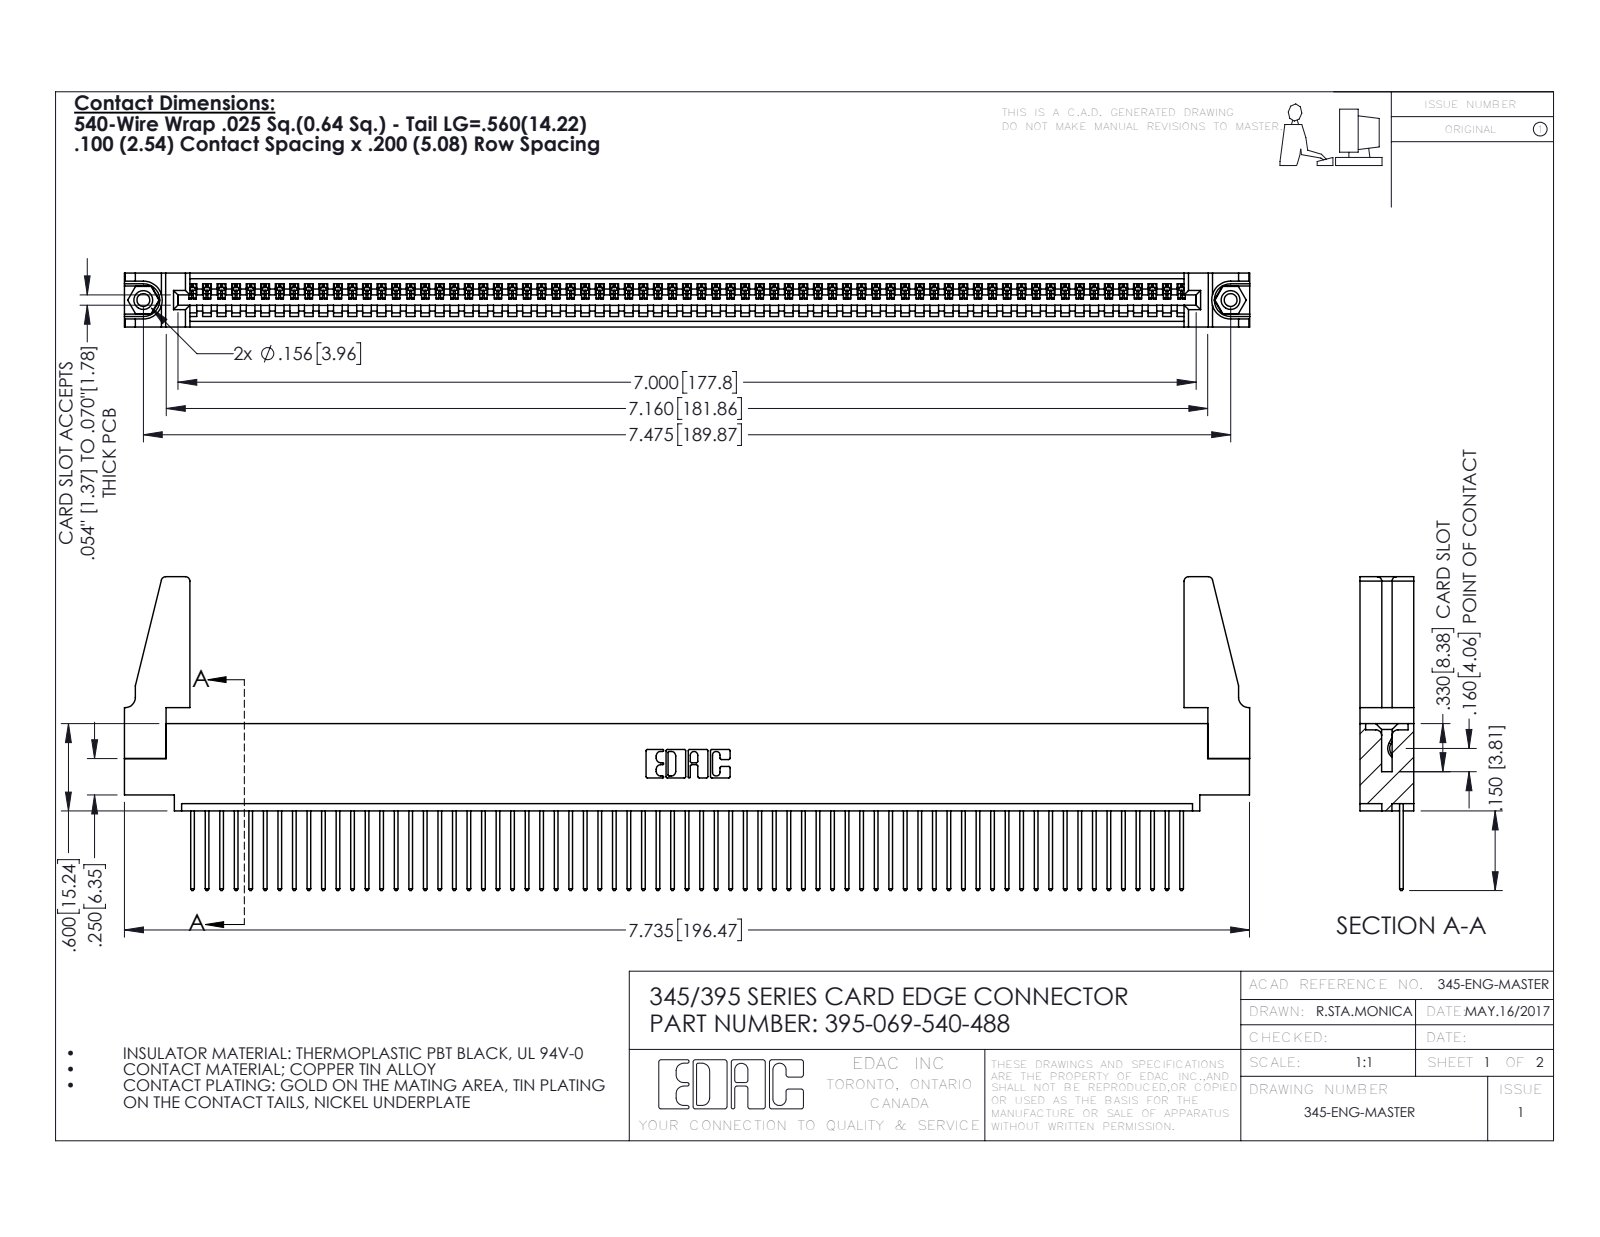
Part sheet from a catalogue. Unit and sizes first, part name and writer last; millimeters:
Units: millimetres
Overall size (bounding box): 196.5 × 54.8 × 9.4
Round holes (diameter × count): ⌀2.3 ×2, ⌀3.2 ×2, ⌀4 ×2, ⌀1.6 ×1
Round bosses / shafts (diameter × count): ⌀3.9 ×2
Partial cylindrical surfaces — rounded edges, fillets, slot ends (radius × count): R0.2 ×138, R0.3 ×138, R0.3 ×22, R0.8 ×8, R0.2 ×6, R0.8 ×6, R0.7 ×3, R0.8 ×2
Main face-to-face distances: 1.8, 7.6, 9.4, 2.5, 6.9, 0.6, 5.1, 5.7, 3.8, 1.8
Hole centre spacings: 6.9, 183.9, 189.9
Volume: 22 160 mm³ · Surface area: 29 370 mm²
Bodies: 74 solids, 4256 faces (2916 planar, 1324 cylindrical, 16 other)
Part name (STEP PRODUCT): 395-069-540-488; 345-250-001_345-250-001-102; 345-220-078_345-220-088; 345 Part_0.110 Offset - 0.156 Dia-TH (+1 more)
STEP written by: SolidWorks 2016 (CONFIG_CONTROL_DESIGN)
